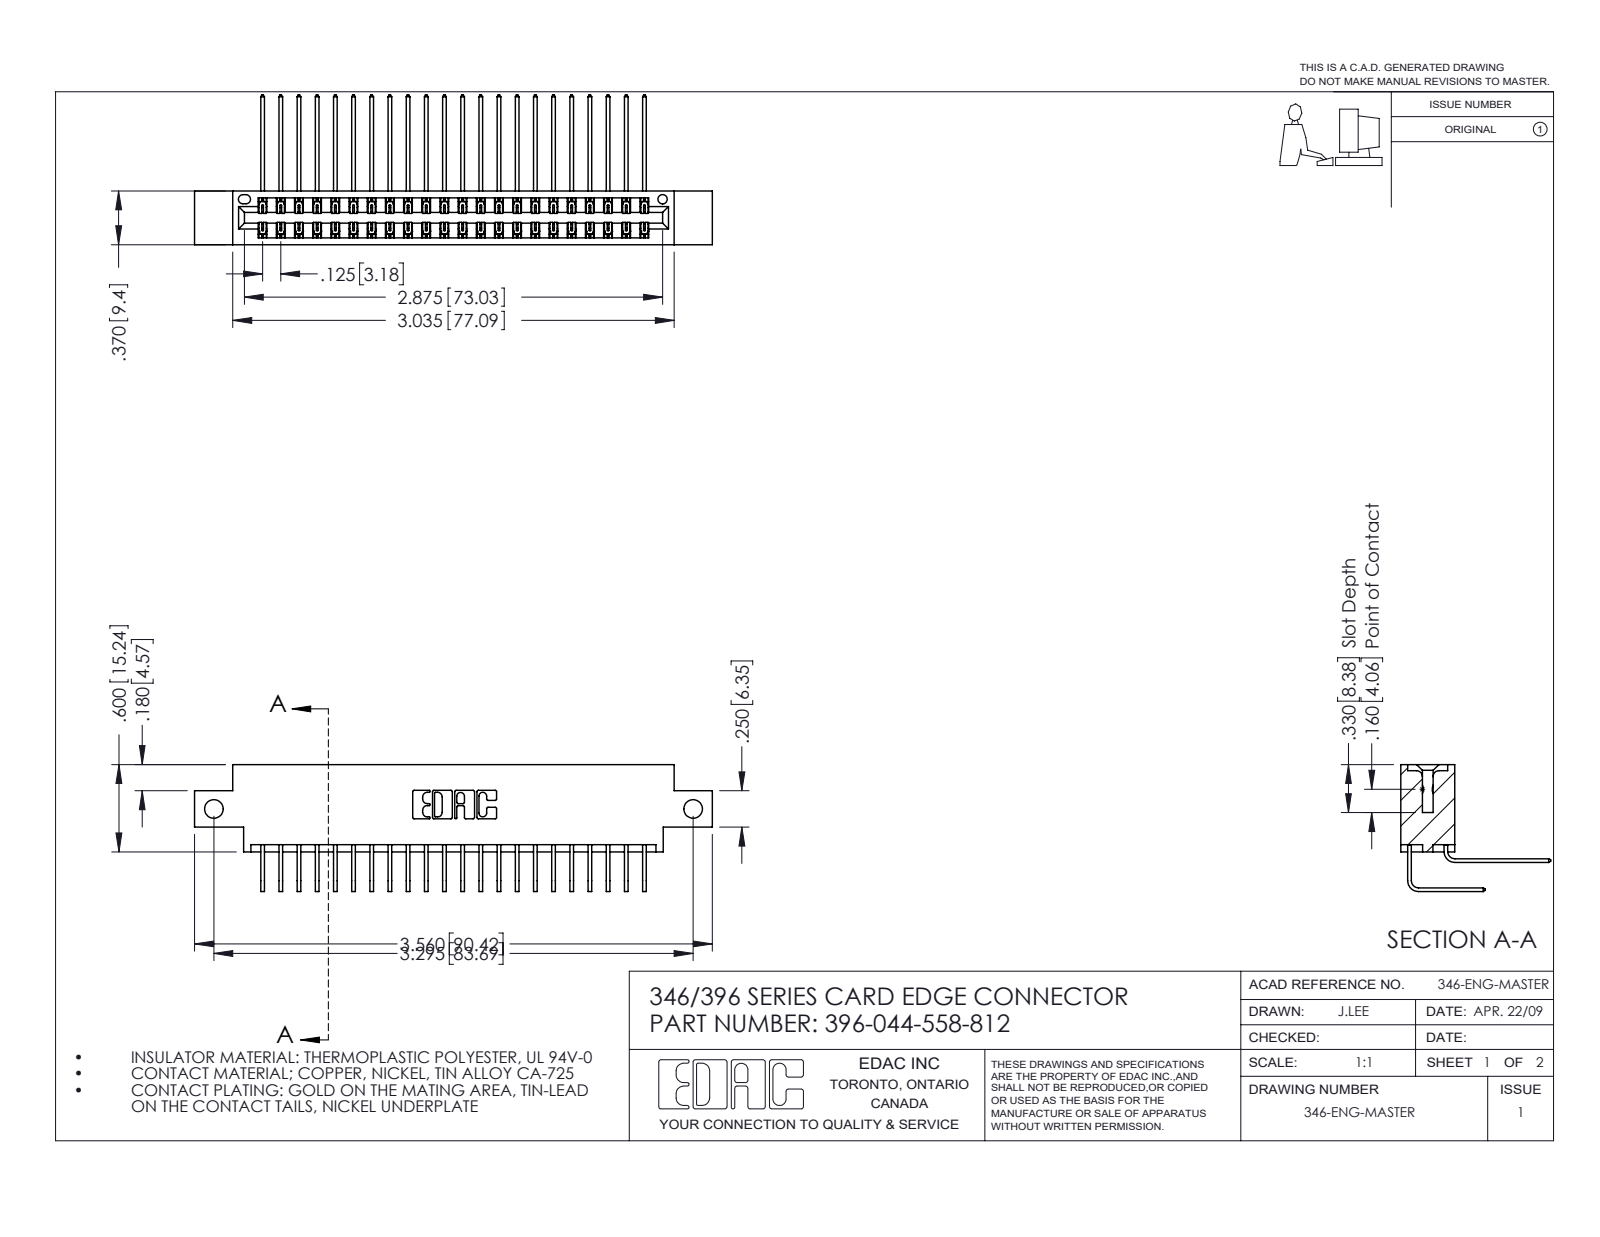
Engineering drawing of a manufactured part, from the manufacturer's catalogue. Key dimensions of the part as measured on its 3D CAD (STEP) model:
Part name (STEP PRODUCT): 345-292-001_558 Tail - 2; 346 Part_0.170 Offset - Side Mount; 345-292-001_558 559 Tail - 1; 396-044-558-812
STEP written by: SolidWorks 2016 (CONFIG_CONTROL_DESIGN)
Units: inches
Bodies: 45 solids, 2502 faces (1708 planar, 794 cylindrical, 0 other)
Overall size (bounding box): 3.56 × 1.03 × 0.873
Volume: 0.529 in³ · Surface area: 19.95 in²
Round holes (diameter × count): ⌀0.128 ×2, ⌀0.064 ×1
Partial cylindrical surfaces — rounded edges, fillets, slot ends (radius × count): R0.006 ×66, R0.01 ×22, R0.007 ×6, R0.031 ×6, R0.026 ×3, R0.014 ×2, R0.022 ×2, R0.024 ×2
Main face-to-face distances: 0.322, 0.048, 0.37, 0.025, 0.25, 0.298, 0.072, 0.275, 0.148, 0.222
Hole centre spacings: 3.295
